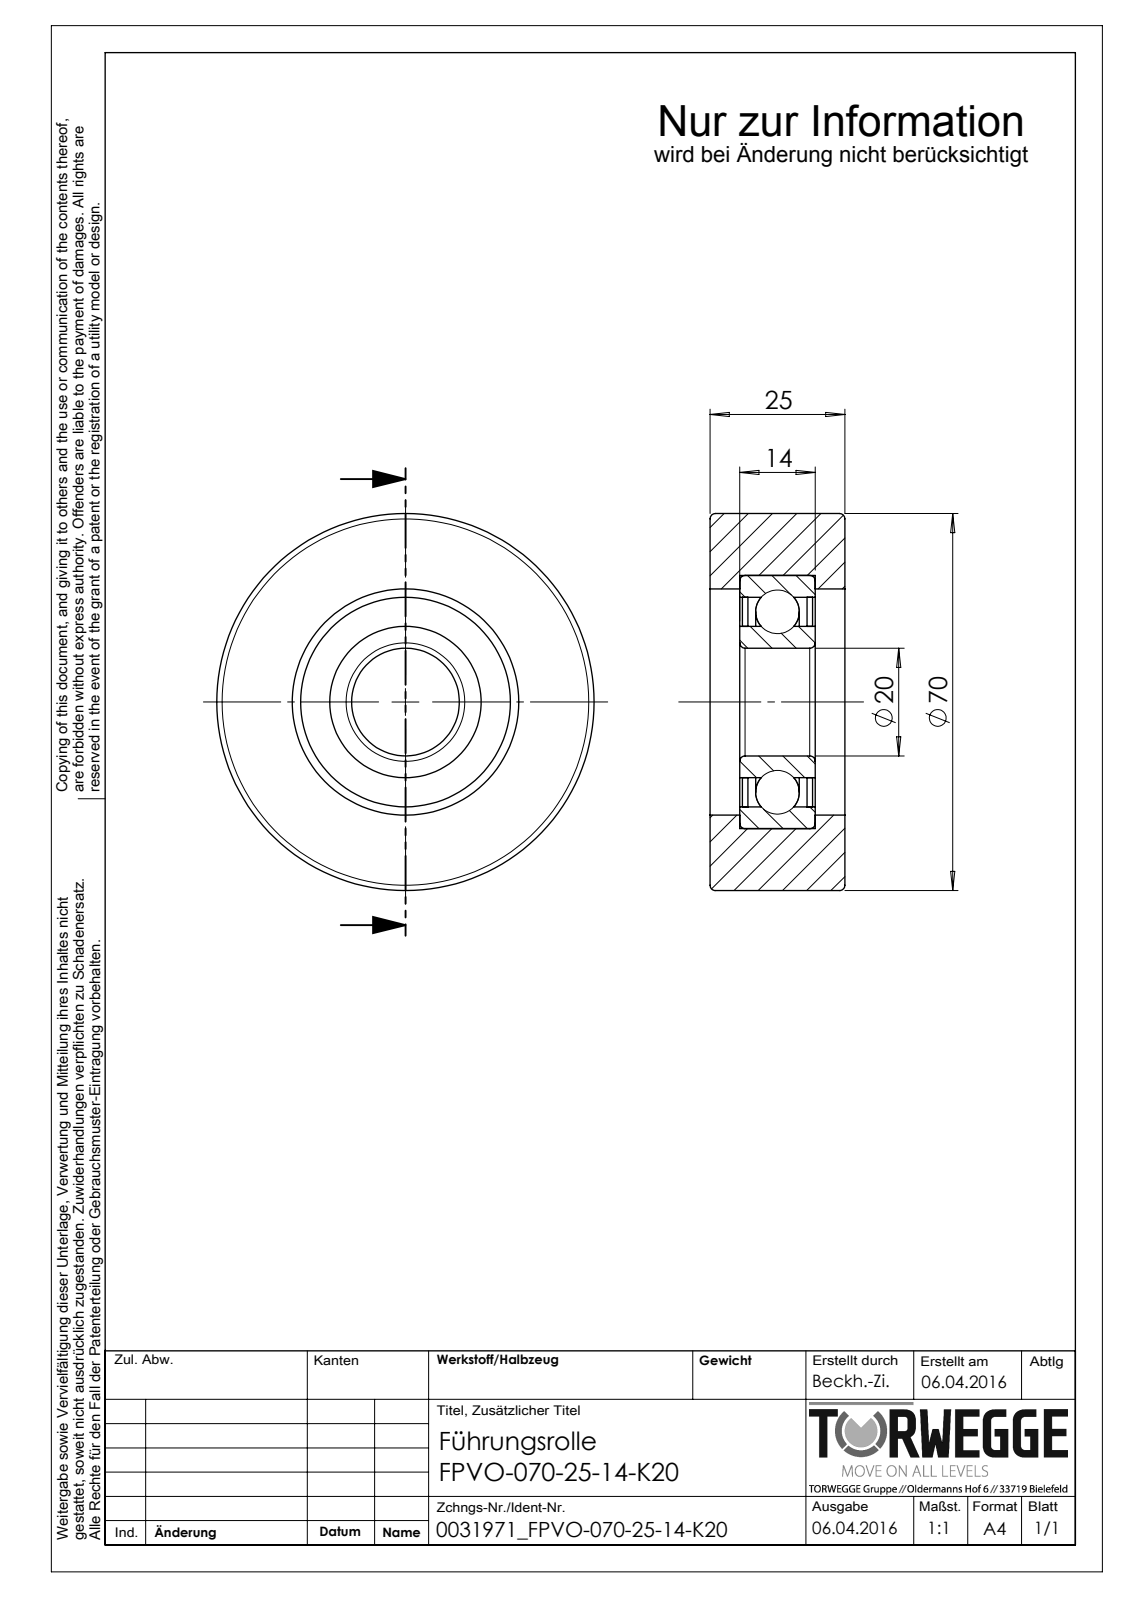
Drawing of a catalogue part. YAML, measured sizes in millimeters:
part_name: "0031971_FPVO-070-25-14-K20"
step_written_by: "SolidWorks 2016 (AUTOMOTIVE_DESIGN)"
units: millimeters
bodies: {solids: 4, faces: 56, planar: 12, cylindrical: 28, other: 16}
overall_size: [70, 70, 25]
volume: 73804
surface_area: 24537
round_holes:
  - {diameter: 20, count: 1}
  - {diameter: 28.1, count: 1}
  - {diameter: 38.9, count: 1}
  - {diameter: 42, count: 1}
  - {diameter: 47, count: 1}
round_bosses_or_shafts:
  - {diameter: 70, count: 1}
face_to_face_distances: [25, 5.5, 19.5, 6, 7, 18, 19, 0.5, 1.5, 12.5]
